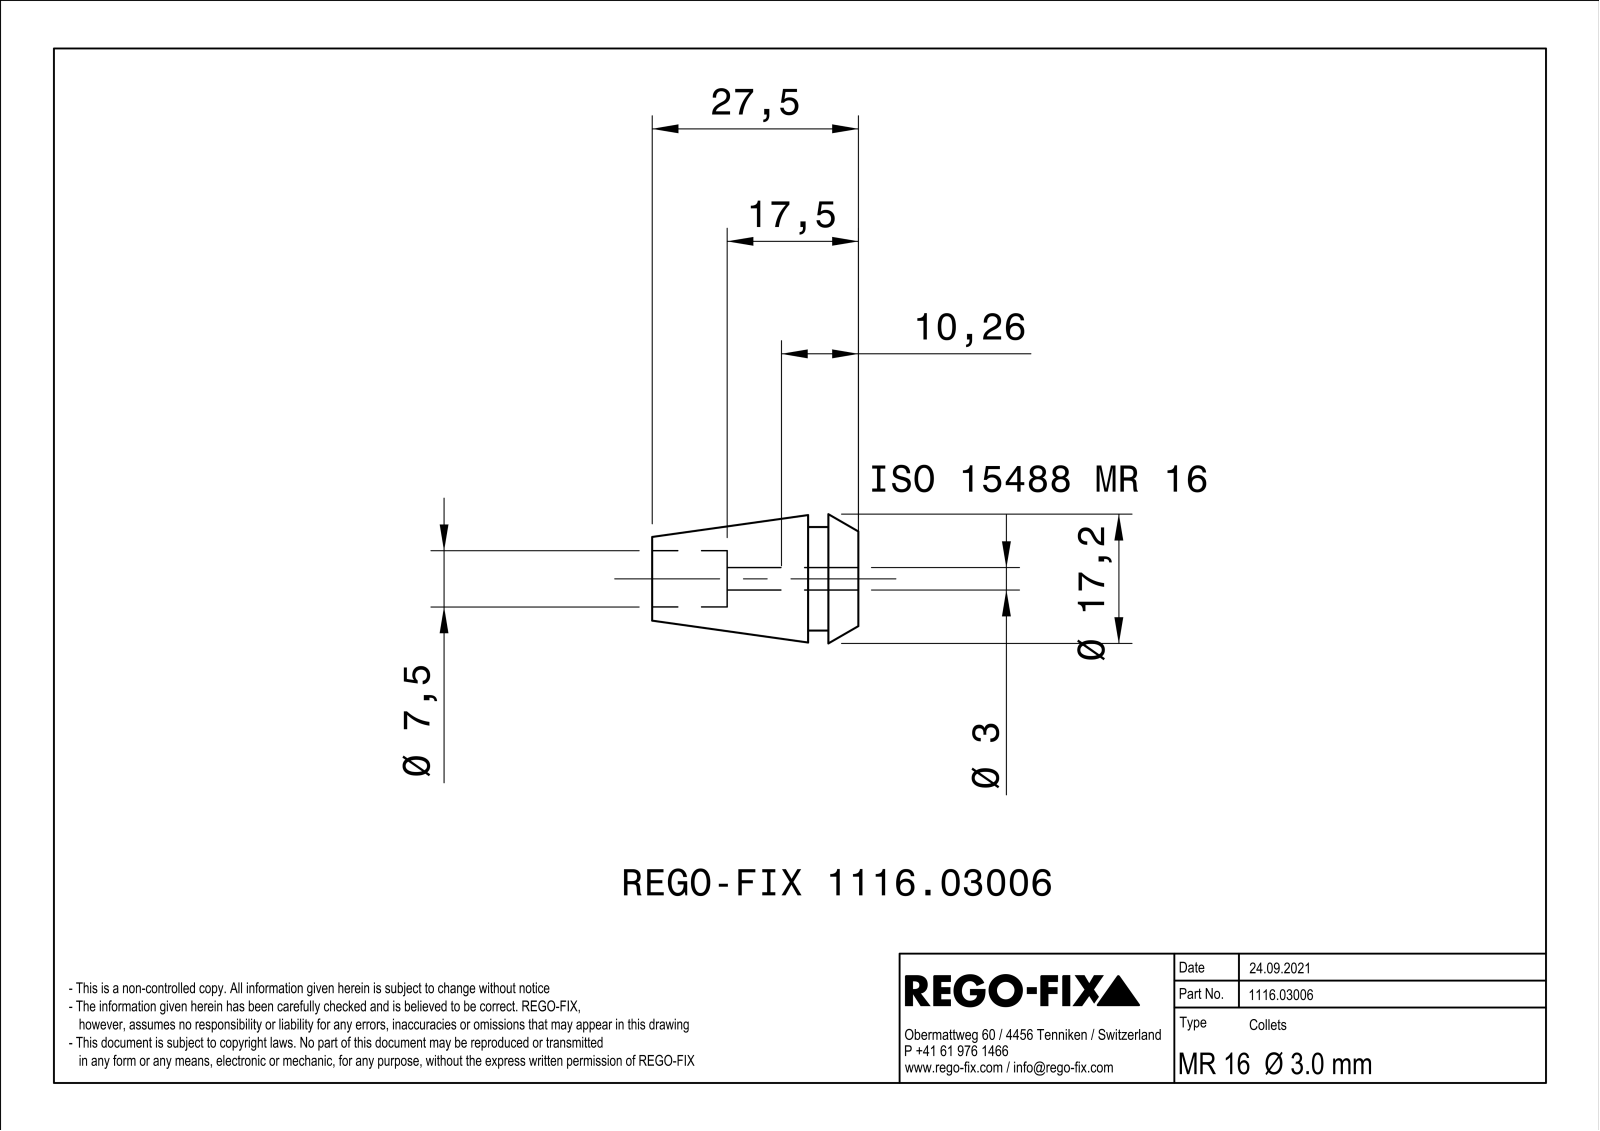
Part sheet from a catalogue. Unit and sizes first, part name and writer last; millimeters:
Units: millimetres
Overall size (bounding box): 27.5 × 16.99 × 16.99
Round holes (diameter × count): ⌀7.5 ×1
Partial cylindrical surfaces — rounded edges, fillets, slot ends (radius × count): R0.3 ×20, R1.5 ×1, R6.9 ×1
Main face-to-face distances: 0.6, 6.7, 4, 2.7, 27.5, 23.5, 20.8, 17.5, 13.5, 10.8
Volume: 2 892 mm³ · Surface area: 4 707 mm²
Bodies: 1 solid, 260 faces (96 planar, 48 cylindrical, 116 other)
Part name (STEP PRODUCT): NOCUT
STEP written by: SIEMENS PLM Software Solid Edge ST10 (AUTOMOTIVE_DESIGN)
